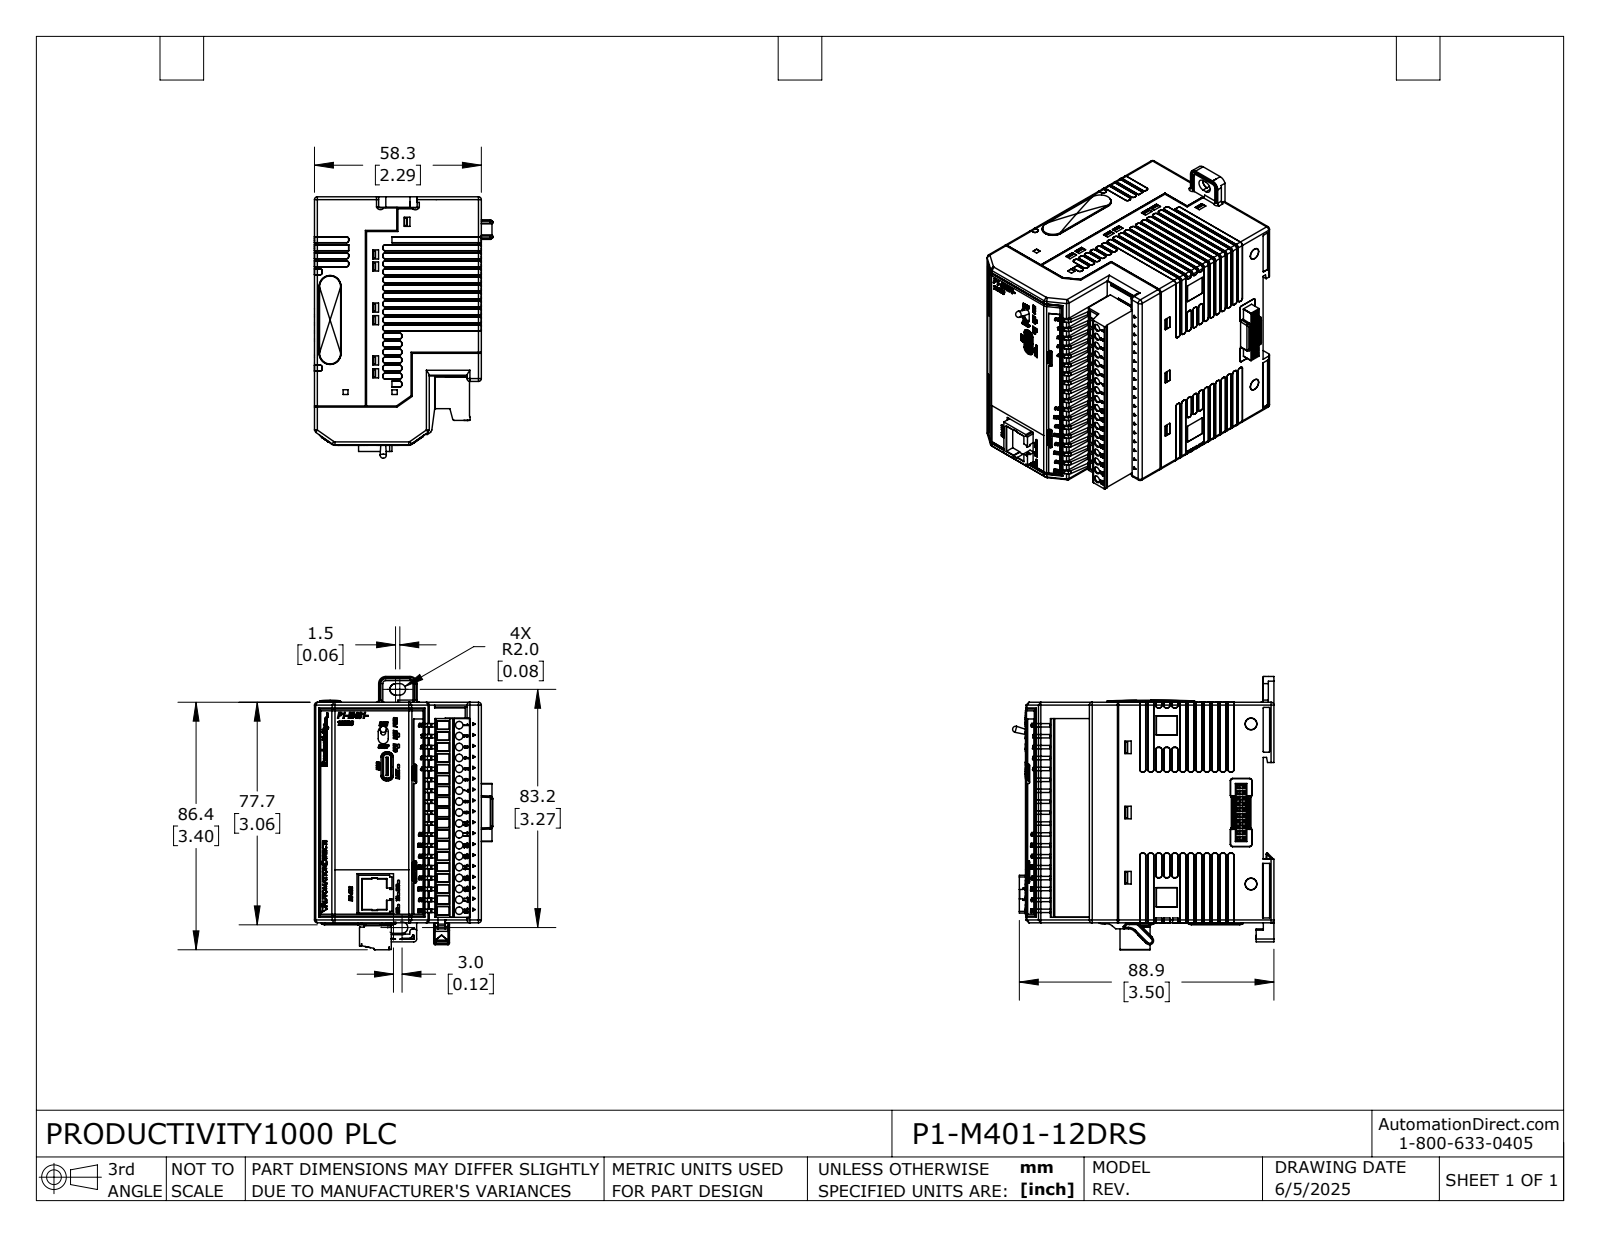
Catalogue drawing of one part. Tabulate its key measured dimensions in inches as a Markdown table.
| quantity | value |
| --- | --- |
| part name | P1-M401-12DRS |
| STEP written by | SolidWorks 2024 (AUTOMOTIVE_DESIGN) |
| units | inches |
| bodies | 21 solids, 3495 faces (1943 planar, 873 cylindrical, 679 other) |
| overall size | 3.686 × 3.593 × 2.452 |
| volume | 2.083 in³ |
| surface area | 103 in² |
| partial cylindrical surfaces (radius × count) | 0.01 × 172, 0.008 × 78, 0.02 × 53, 0.039 × 33, 0.004 × 10, 0.079 × 8, 0.024 × 7, 0.012 × 4 |
| main face-to-face distances | 2.235, 0.02, 0.039, 2.275, 3.01, 3.022, 2.294, 2.294, 2.255, 3.02 |
